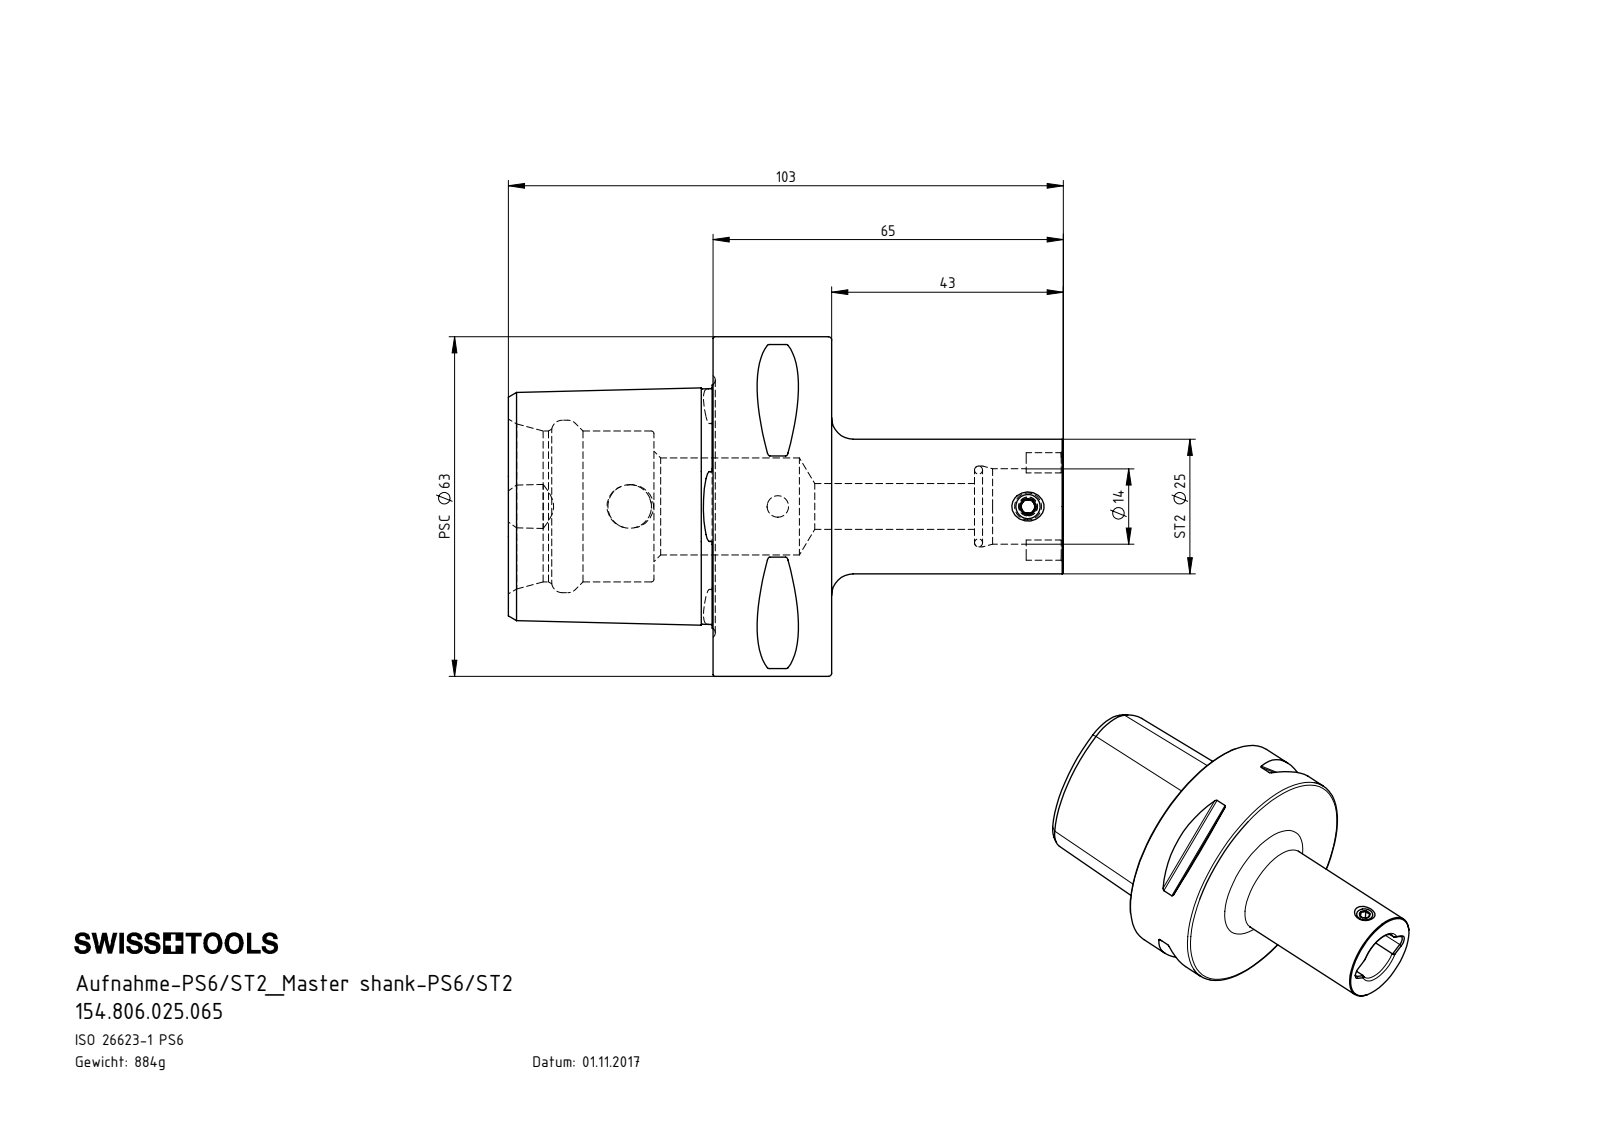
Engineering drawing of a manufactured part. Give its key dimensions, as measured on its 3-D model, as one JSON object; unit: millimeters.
{"part_name": "PS6.ST2.K01.065; ST2-ER1.001.006_A; DIN 3771 - 12x1.5; PS6-ST2.K01.065_B", "step_written_by": "SolidWorks 2017 (AUTOMOTIVE_DESIGN)", "units": "millimeters", "bodies": {"solids": 3, "faces": 133, "planar": 43, "cylindrical": 26, "other": 64}, "overall_size": [103, 63, 63], "volume_mm3": 112658, "surface_area_mm2": 25060, "round_holes": [[2.5, 1], [4, 1], [4.5, 1], [8.1, 1], [8.5, 1], [14, 1], [15, 1], [18, 1], [28, 1], [32, 1]], "round_bosses_or_shafts": [[63, 1], [25, 1], [5, 1]], "partial_cylinders_radius": [[0.5, 8], [1.8, 2], [6, 1]], "face_to_face_distances": [22, 38, 60, 24.88, 103, 65, 43, 27, 11, 33], "hole_center_spacings": [27.5, 46.45, 73.95]}
